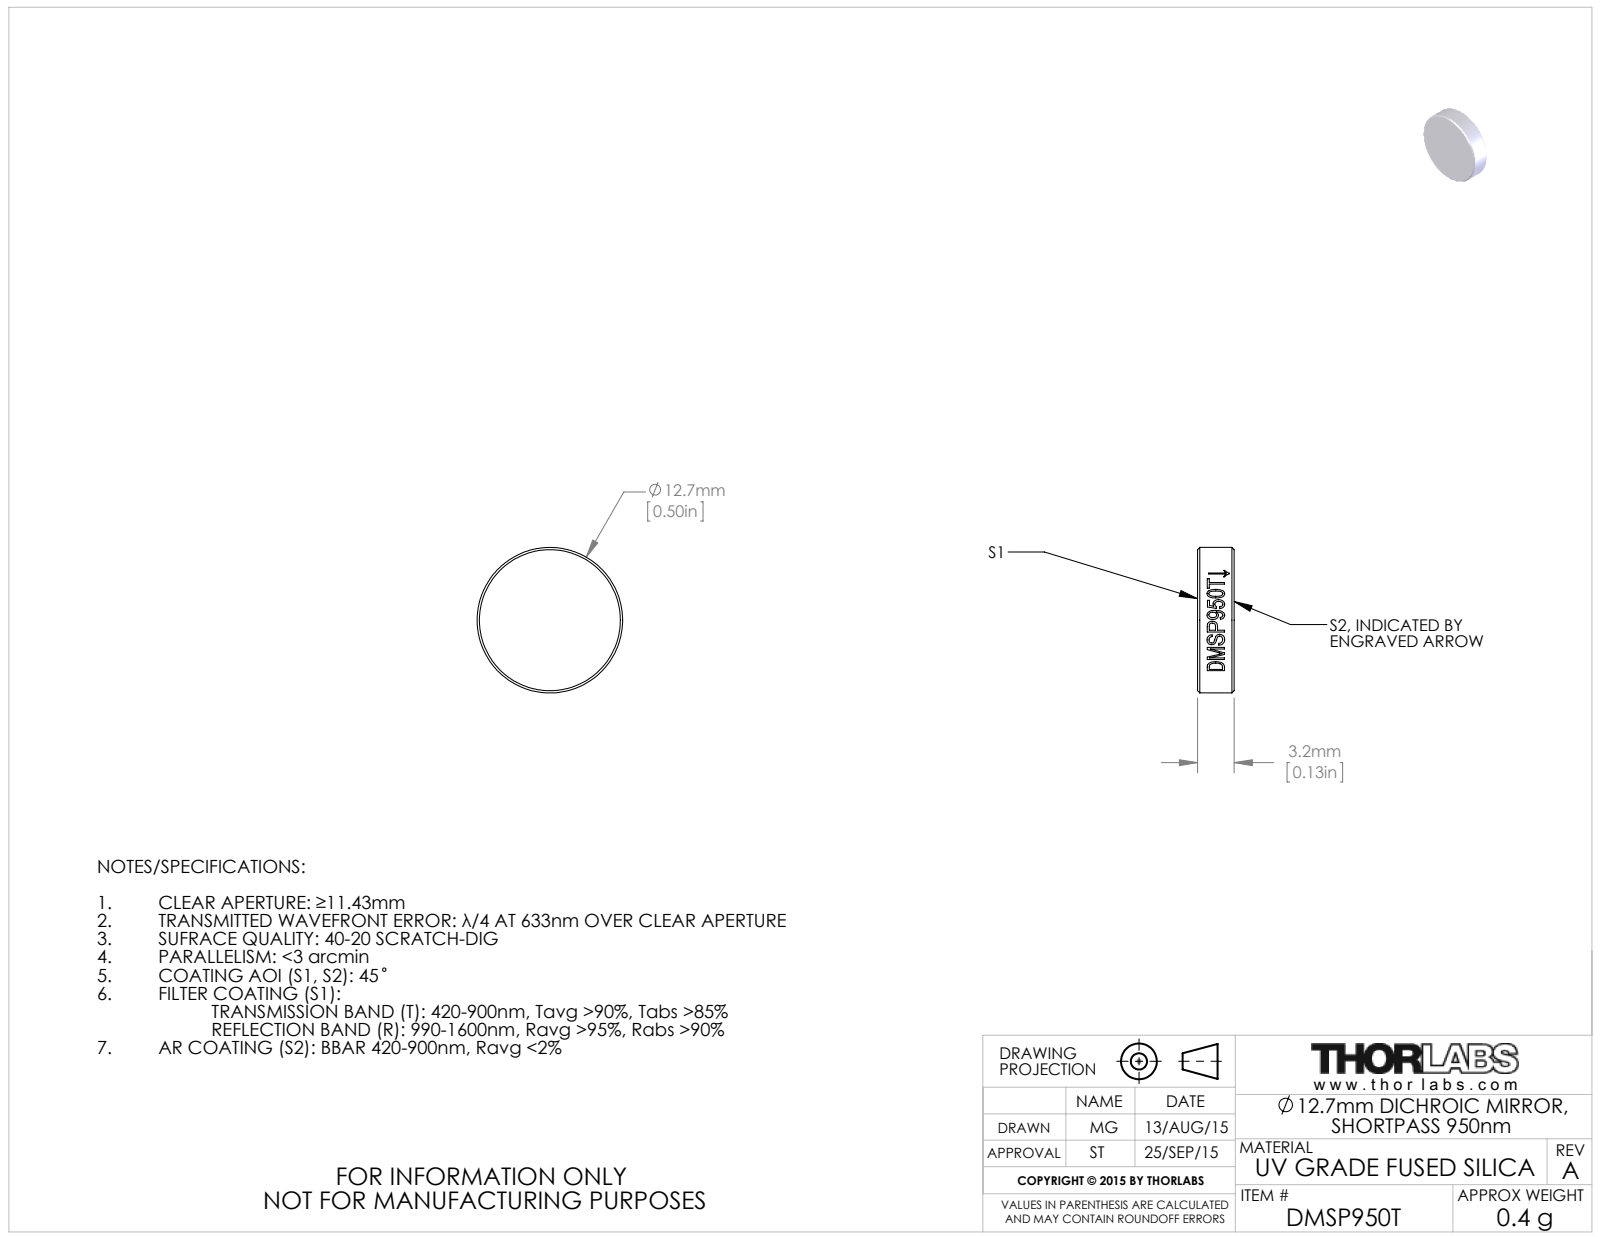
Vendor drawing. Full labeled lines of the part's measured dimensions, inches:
Part name (STEP PRODUCT): TTN045009-E0W
STEP written by: SolidWorks 2014 (CONFIG_CONTROL_DESIGN)
Units: inches
Bodies: 1 solid, 21 faces (2 planar, 15 cylindrical, 4 other)
Overall size (bounding box): 0.5 × 0.5 × 0.126
Volume: 0.025 in³ · Surface area: 0.577 in²
Round bosses / shafts (diameter × count): ⌀0.5 ×1
Main face-to-face distances: 0.126
